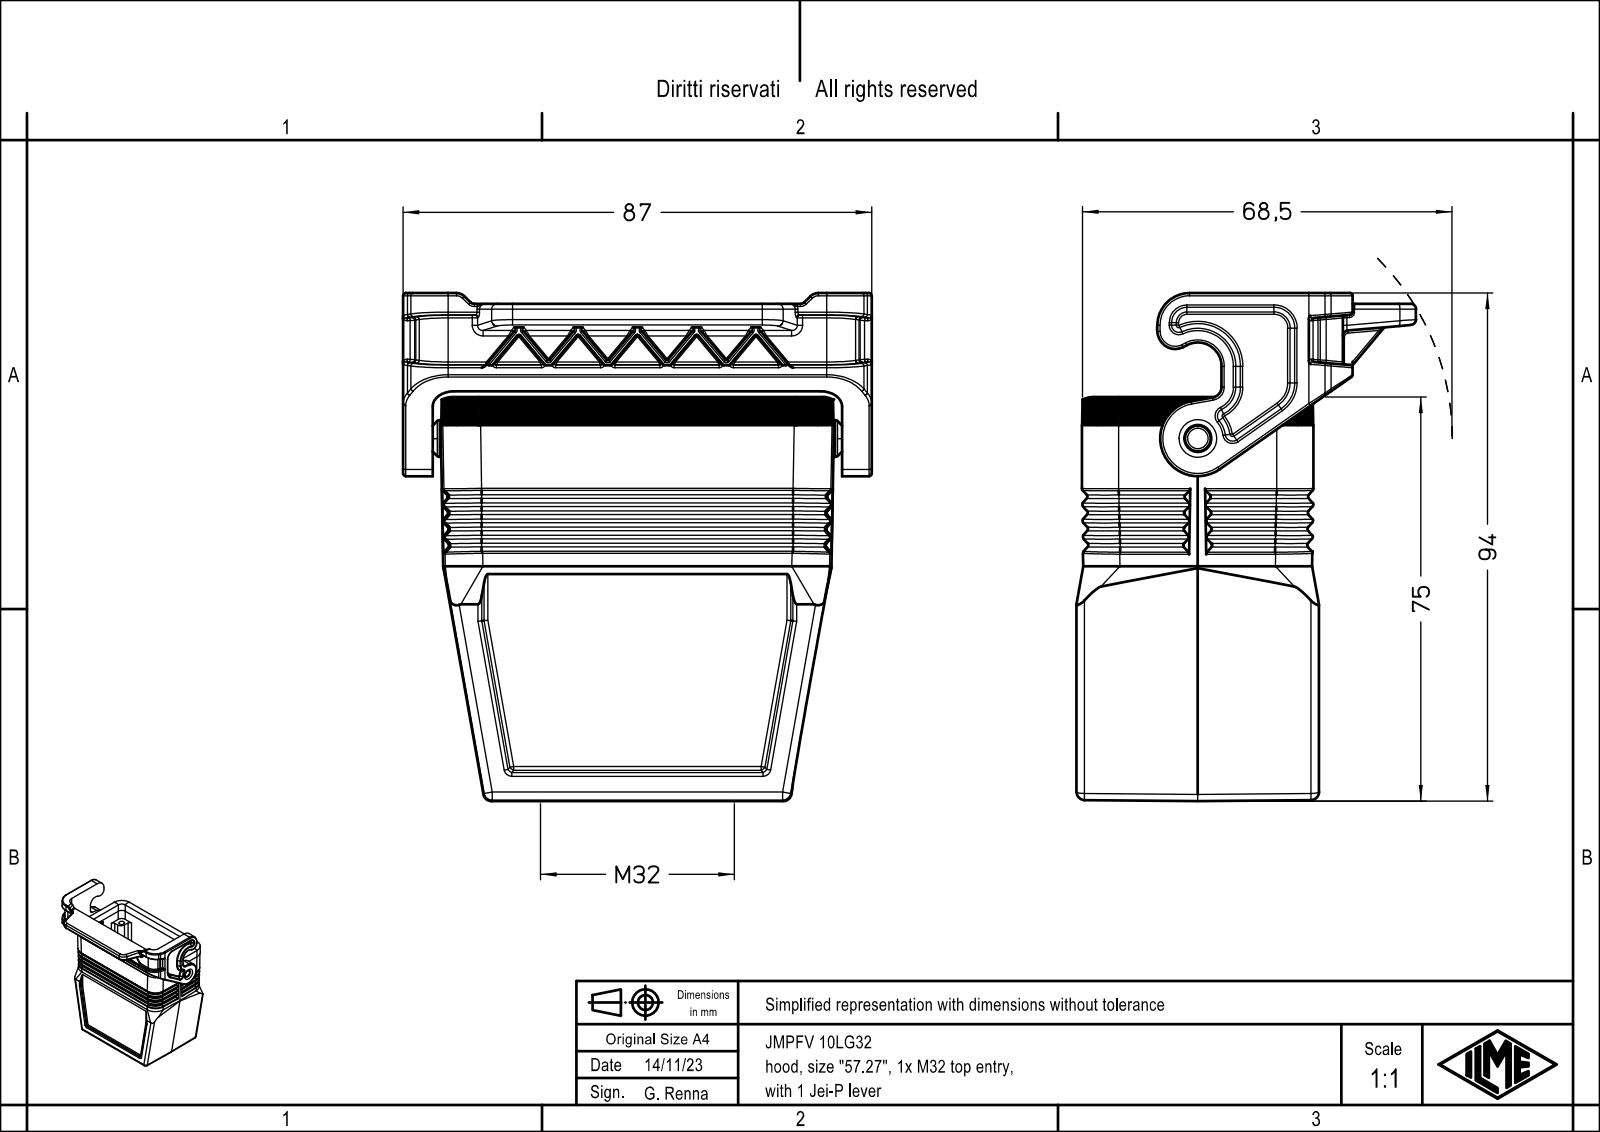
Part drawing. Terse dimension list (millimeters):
name: JMPFV 10LG32
written by: Creo Elements/Direct Modeling 20.1B 02-Apr-2019 (C) Parametric Technology GmbH (AUTOMOTIVE_DESIGN)
unit: mm
bodies: 1 solid, 998 faces (269 planar, 355 cylindrical, 374 other)
size: 94.25 × 87 × 63
volume: 87 168 mm³; area: 43 869 mm²
holes: 4× ⌀3, 4× ⌀3.5, 1× ⌀4.8, 1× ⌀30.6
bosses: 1× ⌀6.8
rounds: 96× R0.5, 71× R0.3, 35× R1, 24× R1.5, 15× R0.33, 13× R7, 12× R3, 8× R4
face distances: 39.25, 3.75, 43, 1, 4.75, 7, 34.5, 38.25, 35.5, 2
hole spacings: 31.54, 27, 57, 63.07
